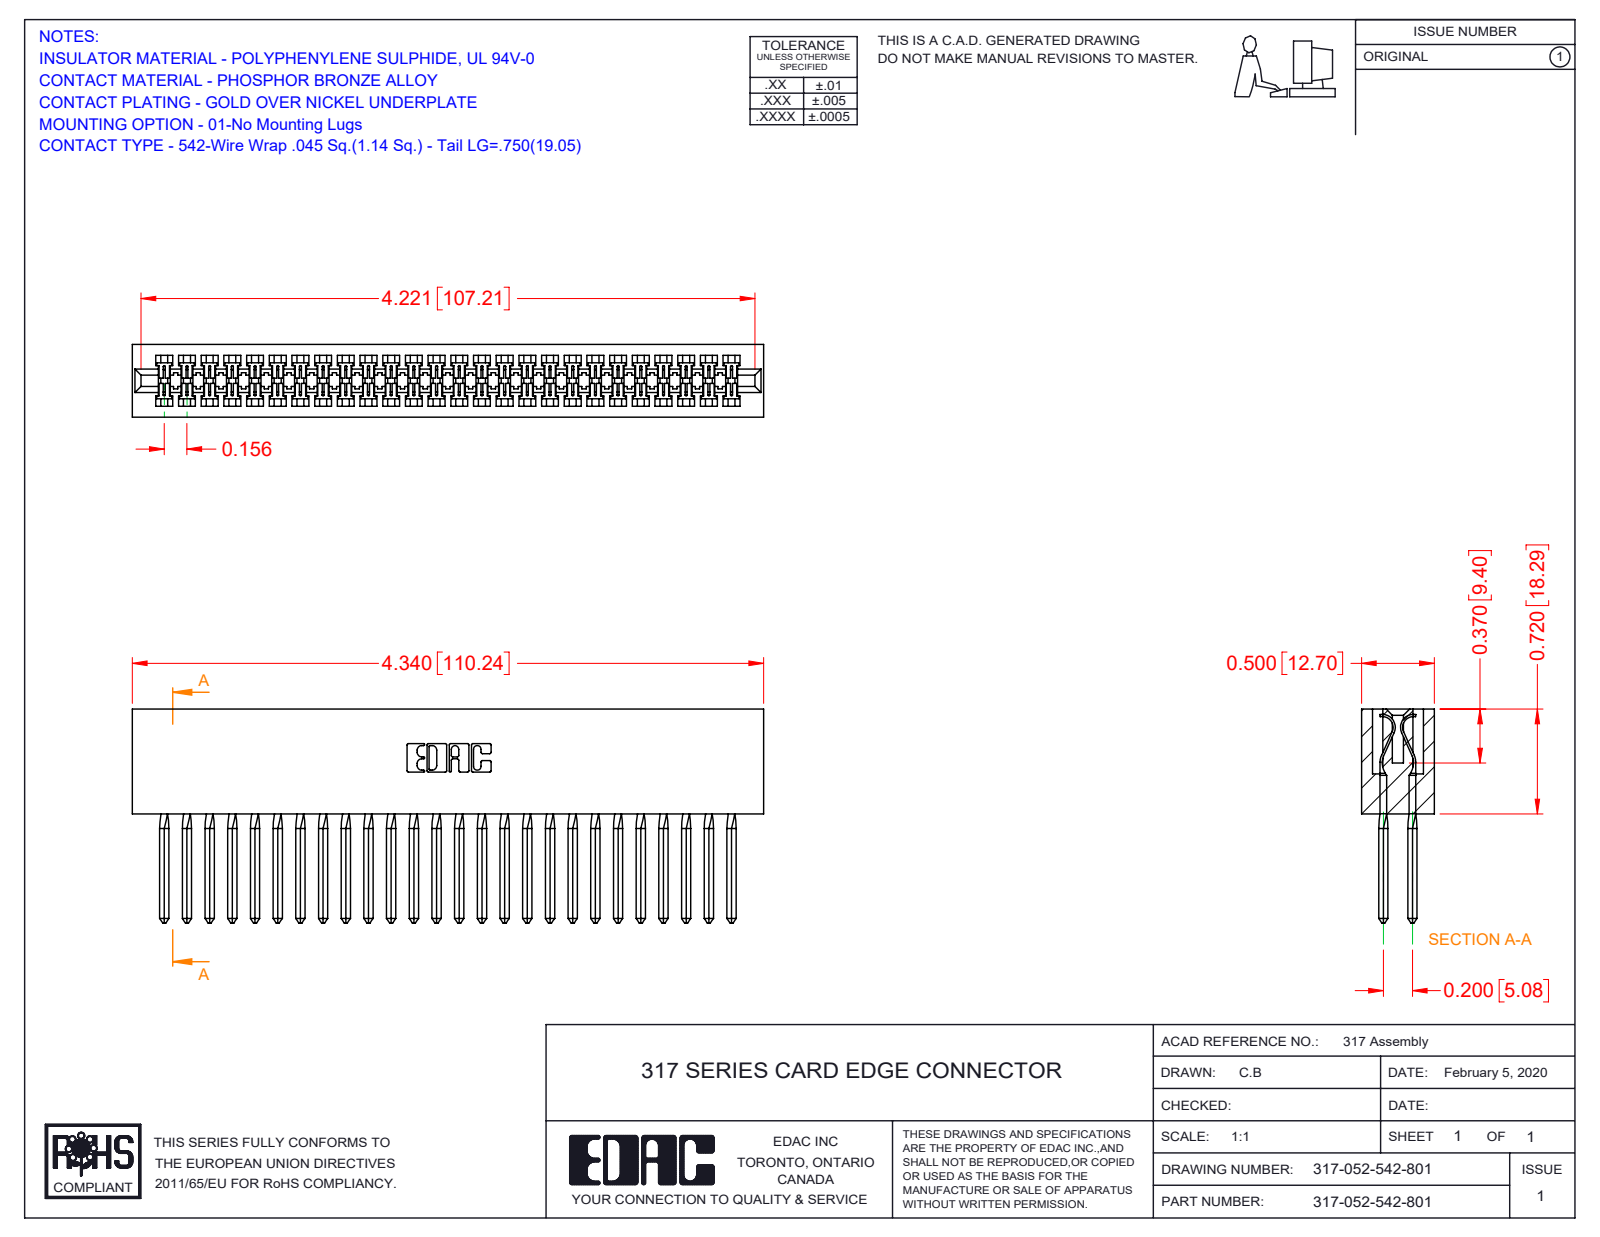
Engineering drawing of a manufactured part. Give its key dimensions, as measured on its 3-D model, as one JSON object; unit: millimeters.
{"part_name": "317 Part_Lugless; 317-052-542-801; 317-290-003_542", "step_written_by": "SolidWorks 2016 (CONFIG_CONTROL_DESIGN)", "units": "millimeters", "bodies": {"solids": 53, "faces": 3054, "planar": 2442, "cylindrical": 404, "other": 208}, "overall_size": [110.2, 37.3, 12.7], "volume_mm3": 19270, "surface_area_mm2": 26460, "partial_cylinders_radius": [[0.2, 104], [0.3, 22], [0.2, 6], [0.8, 6], [0.7, 3], [1.9, 2], [2.3, 2], [2.5, 2]], "face_to_face_distances": [12.7, 1.9, 10.8, 8.9, 5.1, 2.8, 2.9, 1.2, 18.3, 3.5]}
